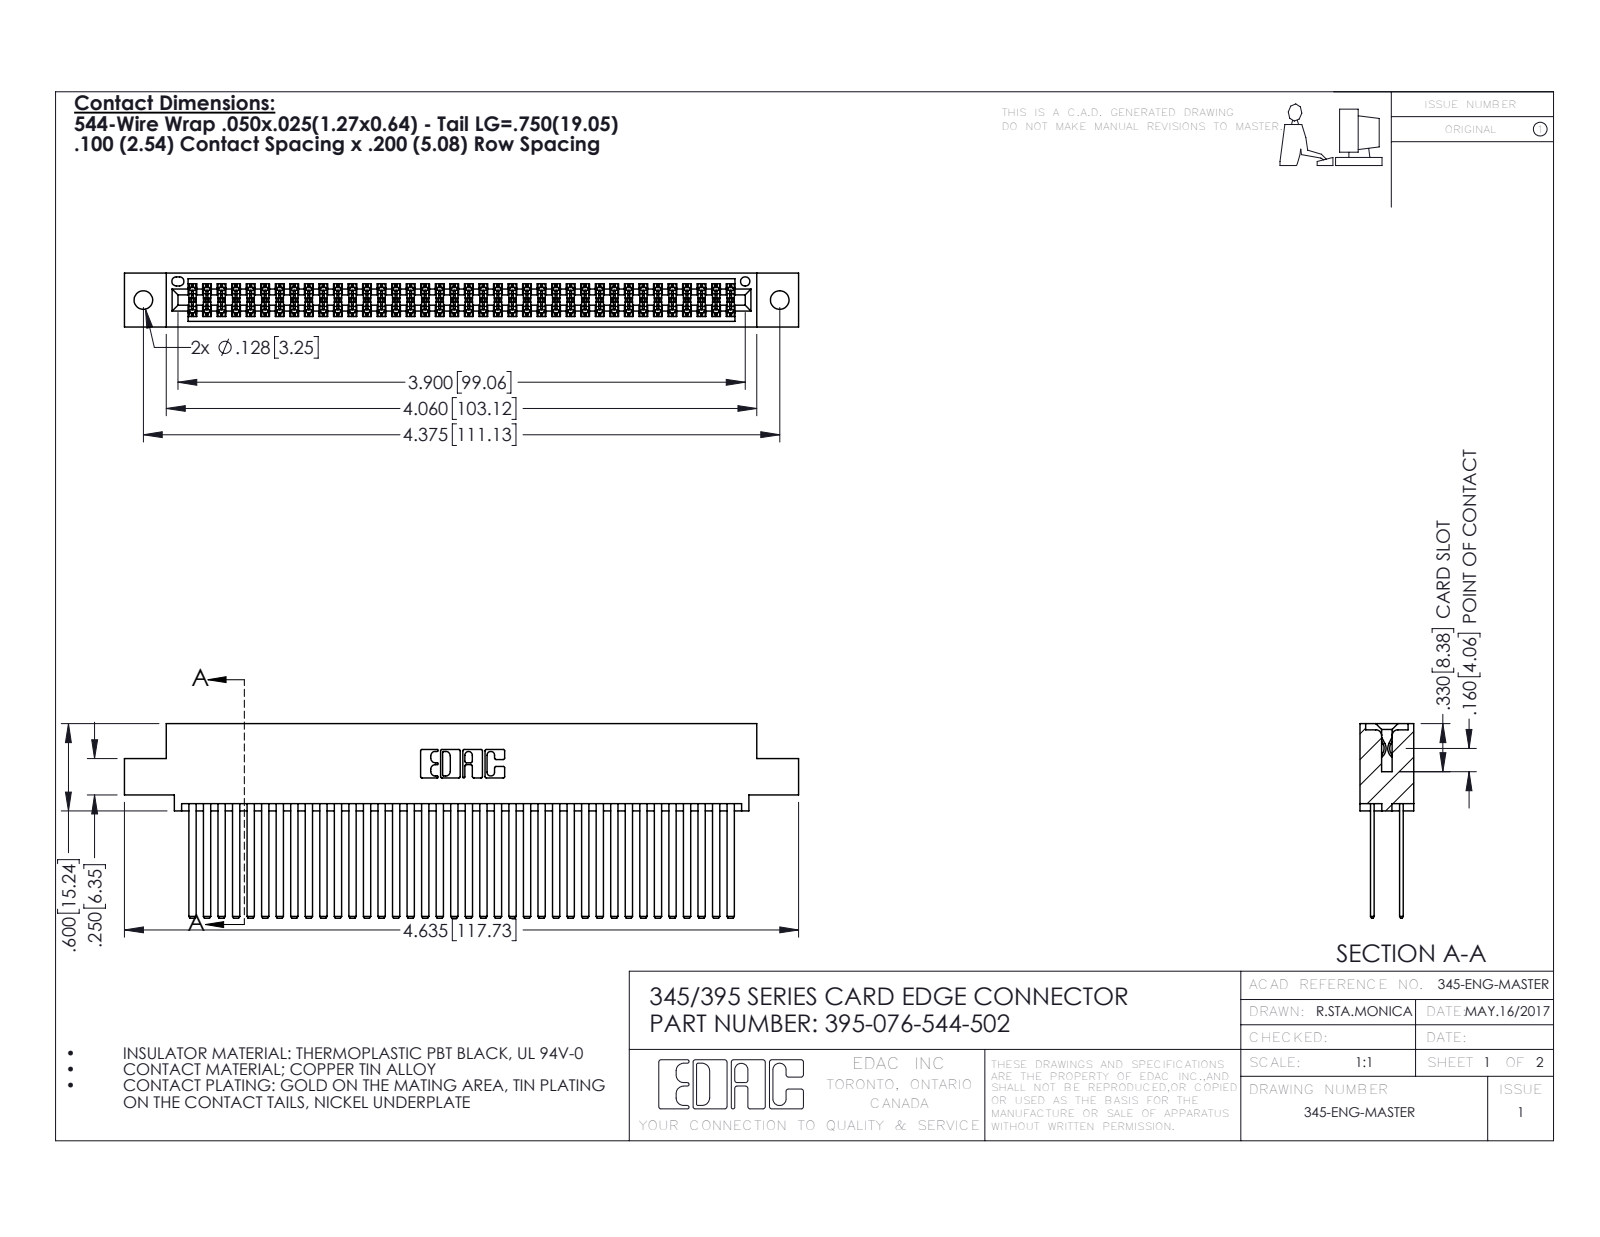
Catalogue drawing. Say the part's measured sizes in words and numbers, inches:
The part is named "345 Part_0.110 Offset - 0.128 Dia; 395-076-544-502; 345-292-001_345-293-144". Its 3-D file was written by "SolidWorks 2016 (CONFIG_CONTROL_DESIGN)". It is 77 solids with 3474 faces: 2288 planar, 1186 cylindrical and 0 other. Overall it measures 4.635 by 1.337 by 0.37 inches. Its volume is 0.754 cubic inches and its surface area 32.75 square inches. Round holes: 2 of diameter 0.128, 1 of diameter 0.064. Partial cylindrical surfaces (rounded edges, fillets, slot ends): 114 of radius 0.006, 22 of radius 0.01, 6 of radius 0.007, 6 of radius 0.031, 3 of radius 0.026, 2 of radius 0.014, 2 of radius 0.019, 2 of radius 0.022. The main face-to-face distances are 0.2, 0.025, 0.298, 0.072, 0.098, 0.272, 0.225, 0.175, 0.37, 0.05. The hole center spacings are 0.27, 4.139, 4.375.
